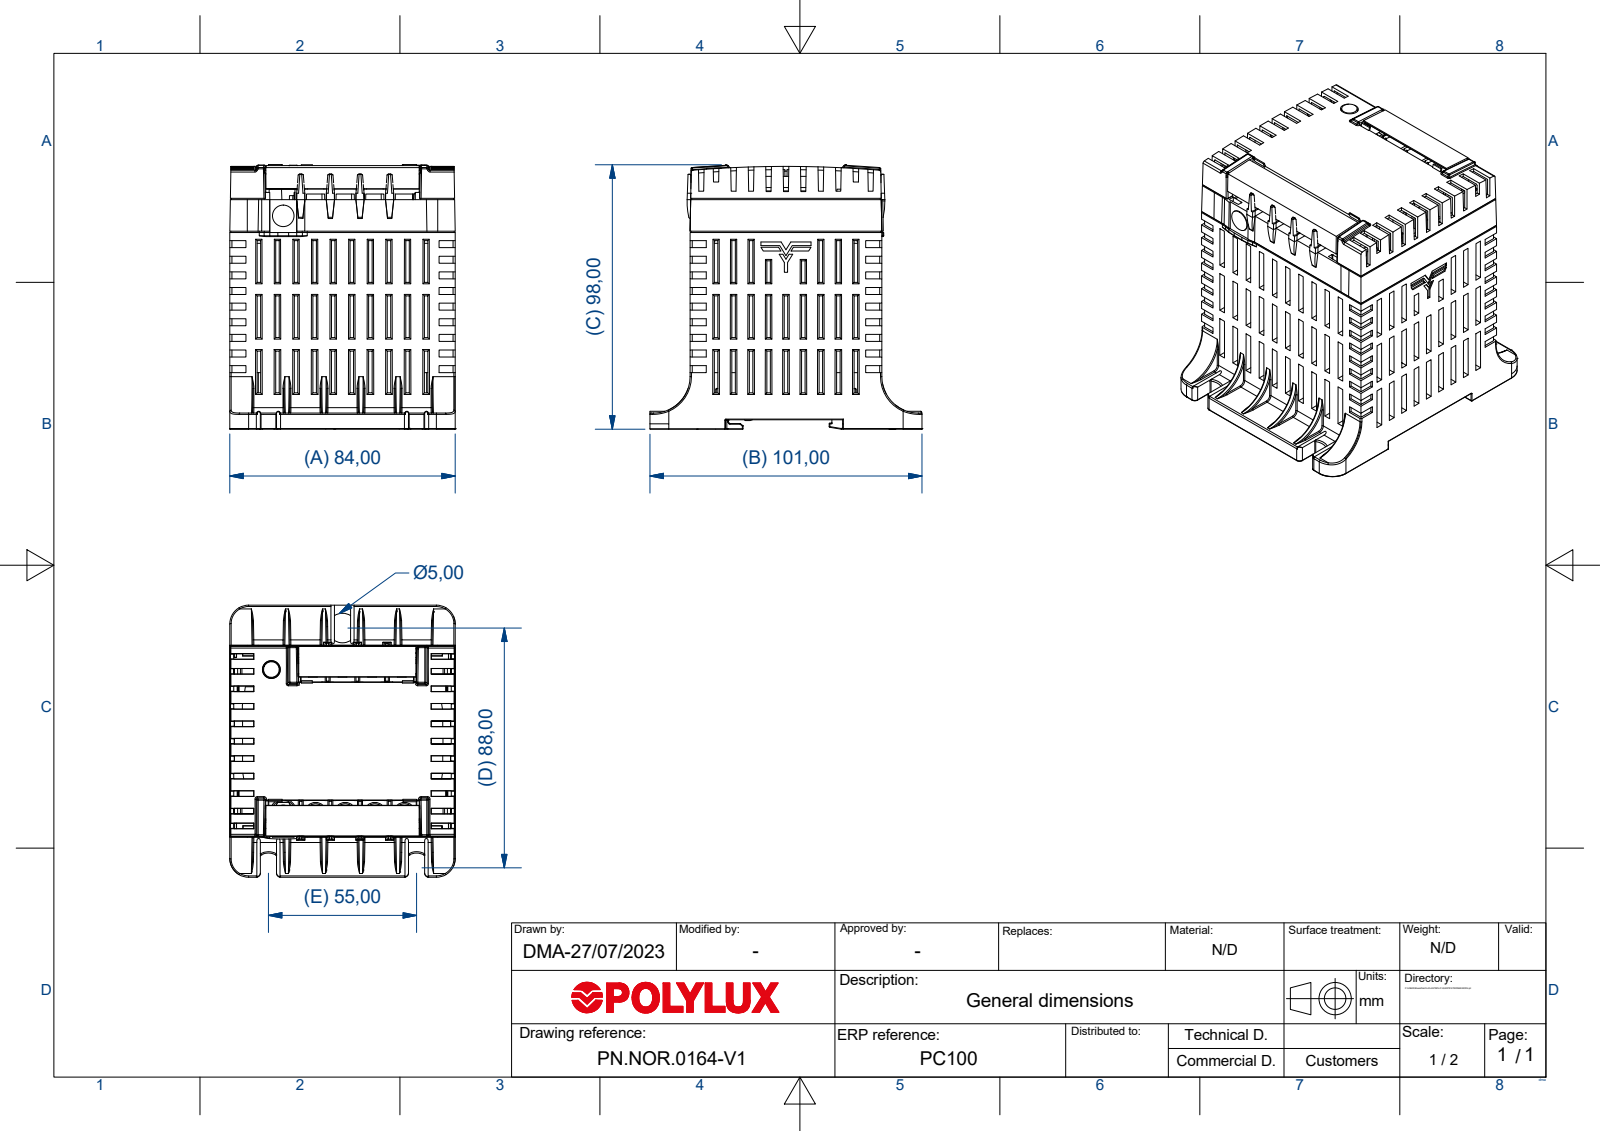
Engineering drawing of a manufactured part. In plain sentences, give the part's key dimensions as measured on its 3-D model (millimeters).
The part is named "RC25". Its 3-D file was written by "Autodesk Inventor 2018 (AUTOMOTIVE_DESIGN)". It is 0 solids with 2769 faces: 1692 planar, 496 cylindrical and 581 other. Overall it measures 101 by 98.46 by 83.7 millimeters. Round holes: 1 of diameter 20. Round bosses or shafts: 1 of diameter 8. Partial cylindrical surfaces (rounded edges, fillets, slot ends): 63 of radius 0.5, 40 of radius 0.35, 40 of radius 0.4, 39 of radius 0.15, 38 of radius 0.25, 24 of radius 0.3, 17 of radius 0.71, 12 of radius 27.54. The main face-to-face distances are 2.5, 83.7, 71.2, 6.8, 20.39, 13.59, 6.79, 6.4, 13.6, 6.41.
